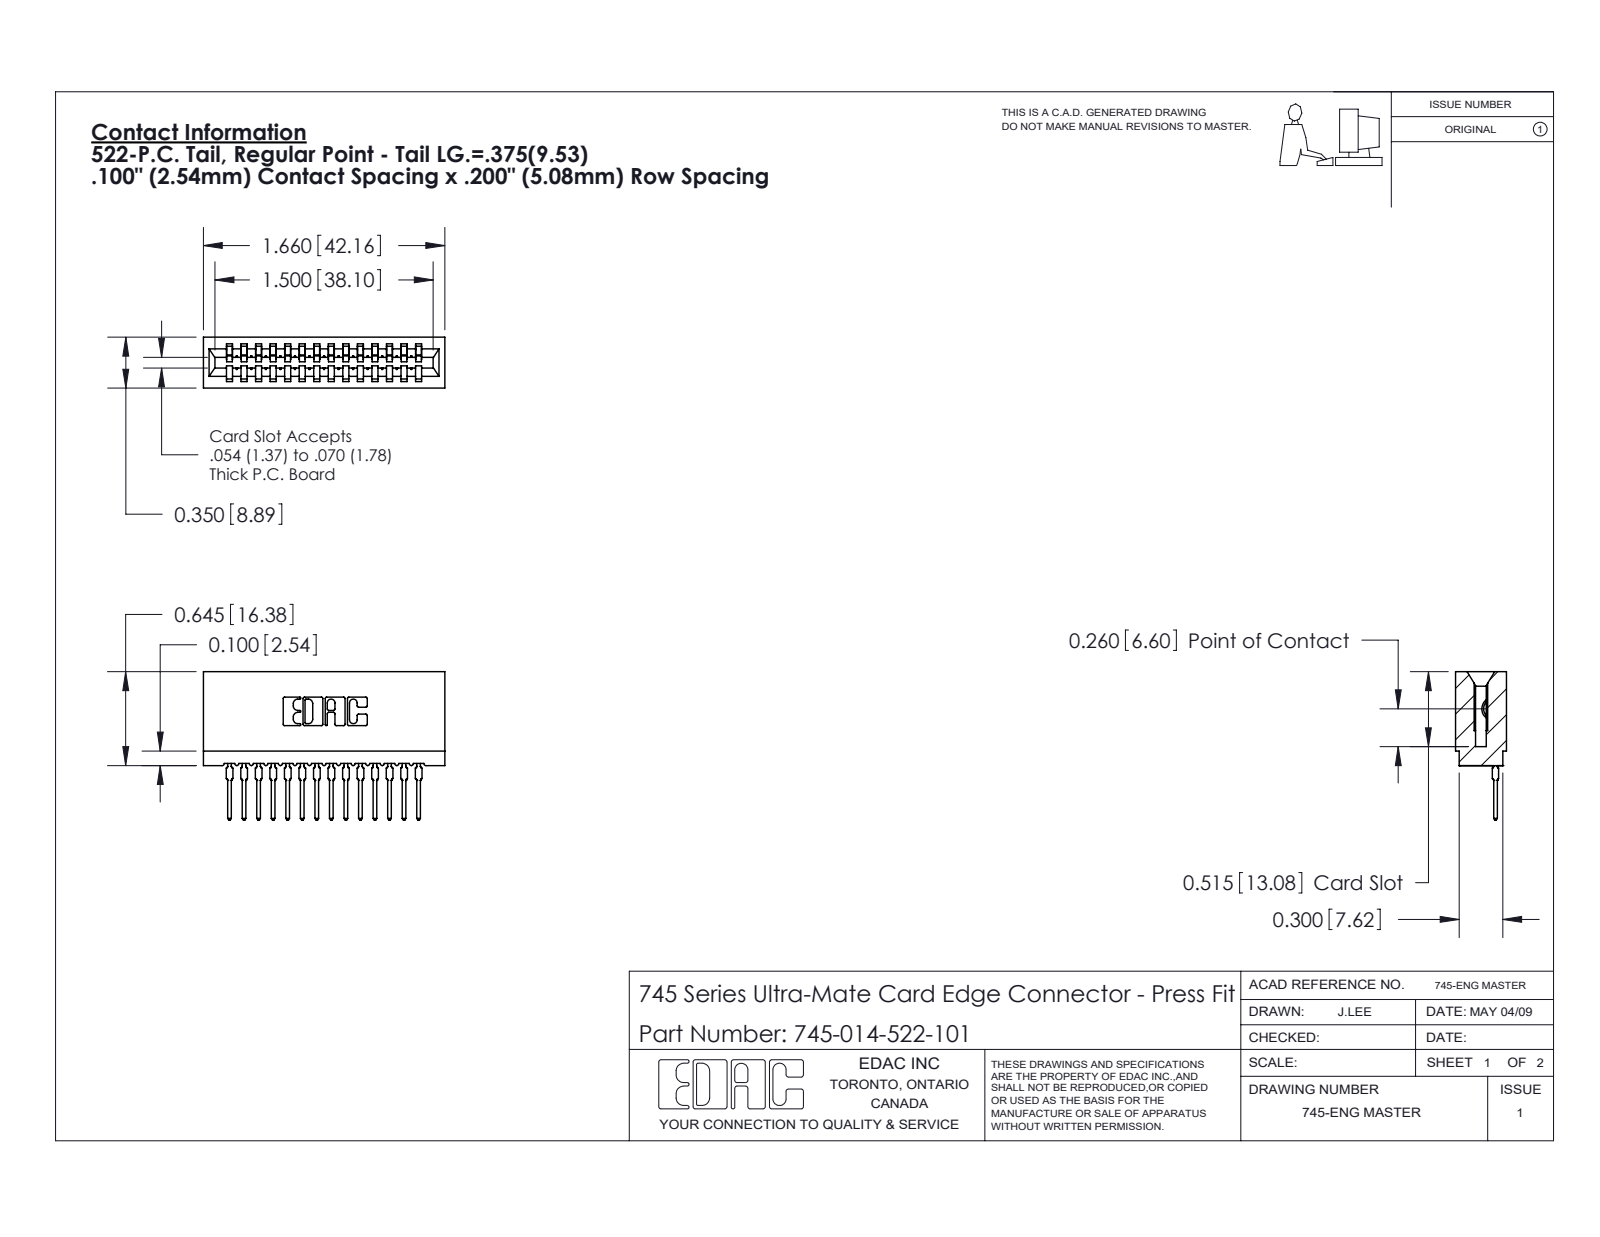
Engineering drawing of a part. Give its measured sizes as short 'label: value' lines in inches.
name: 745-014-522-101; 745-292-001_522; 745 Part_Insulator Option - 01
written by: SolidWorks 2020 (CONFIG_CONTROL_DESIGN)
unit: in
bodies: 15 solids, 1663 faces (993 planar, 306 cylindrical, 364 other)
size: 1.66 × 1.021 × 0.35
volume: 0.235 in³; area: 10.3 in²
rounds: 28× R0.015, 28× R0.021, 22× R0.01, 6× R0.007, 6× R0.031, 4× R0.005, 4× R0.011, 3× R0.026
face distances: 0.1, 0.2, 0.3, 0.4, 0.5, 0.6, 0.7, 0.35, 0.8, 0.138
